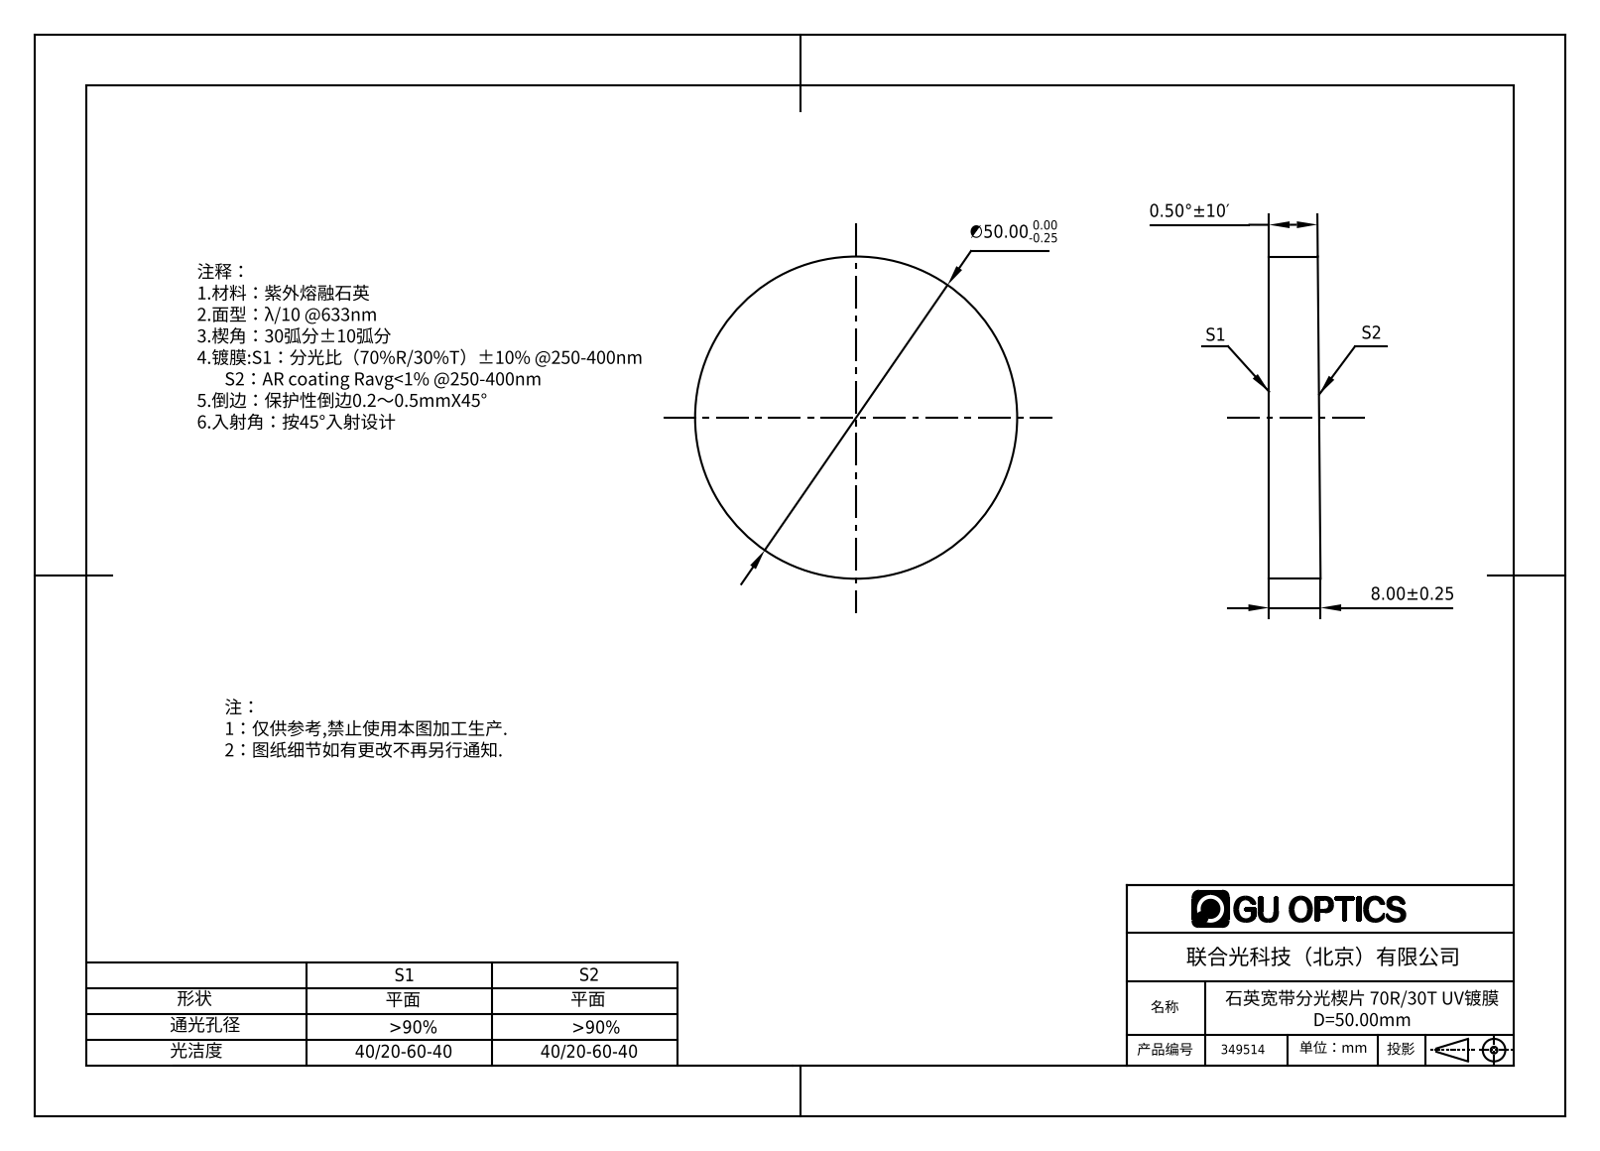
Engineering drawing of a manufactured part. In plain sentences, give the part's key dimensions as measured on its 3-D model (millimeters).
The part is named "349512". Its 3-D file was written by "SolidWorks 2016 (AUTOMOTIVE_DESIGN)". It is 1 solid with 4 faces: 2 planar, 2 cylindrical and 0 other. Overall it measures 50 by 50 by 8 millimeters. Its volume is 15 280 cubic millimeters and its surface area 5 150 square millimeters. Round bosses or shafts: 1 of diameter 50.
